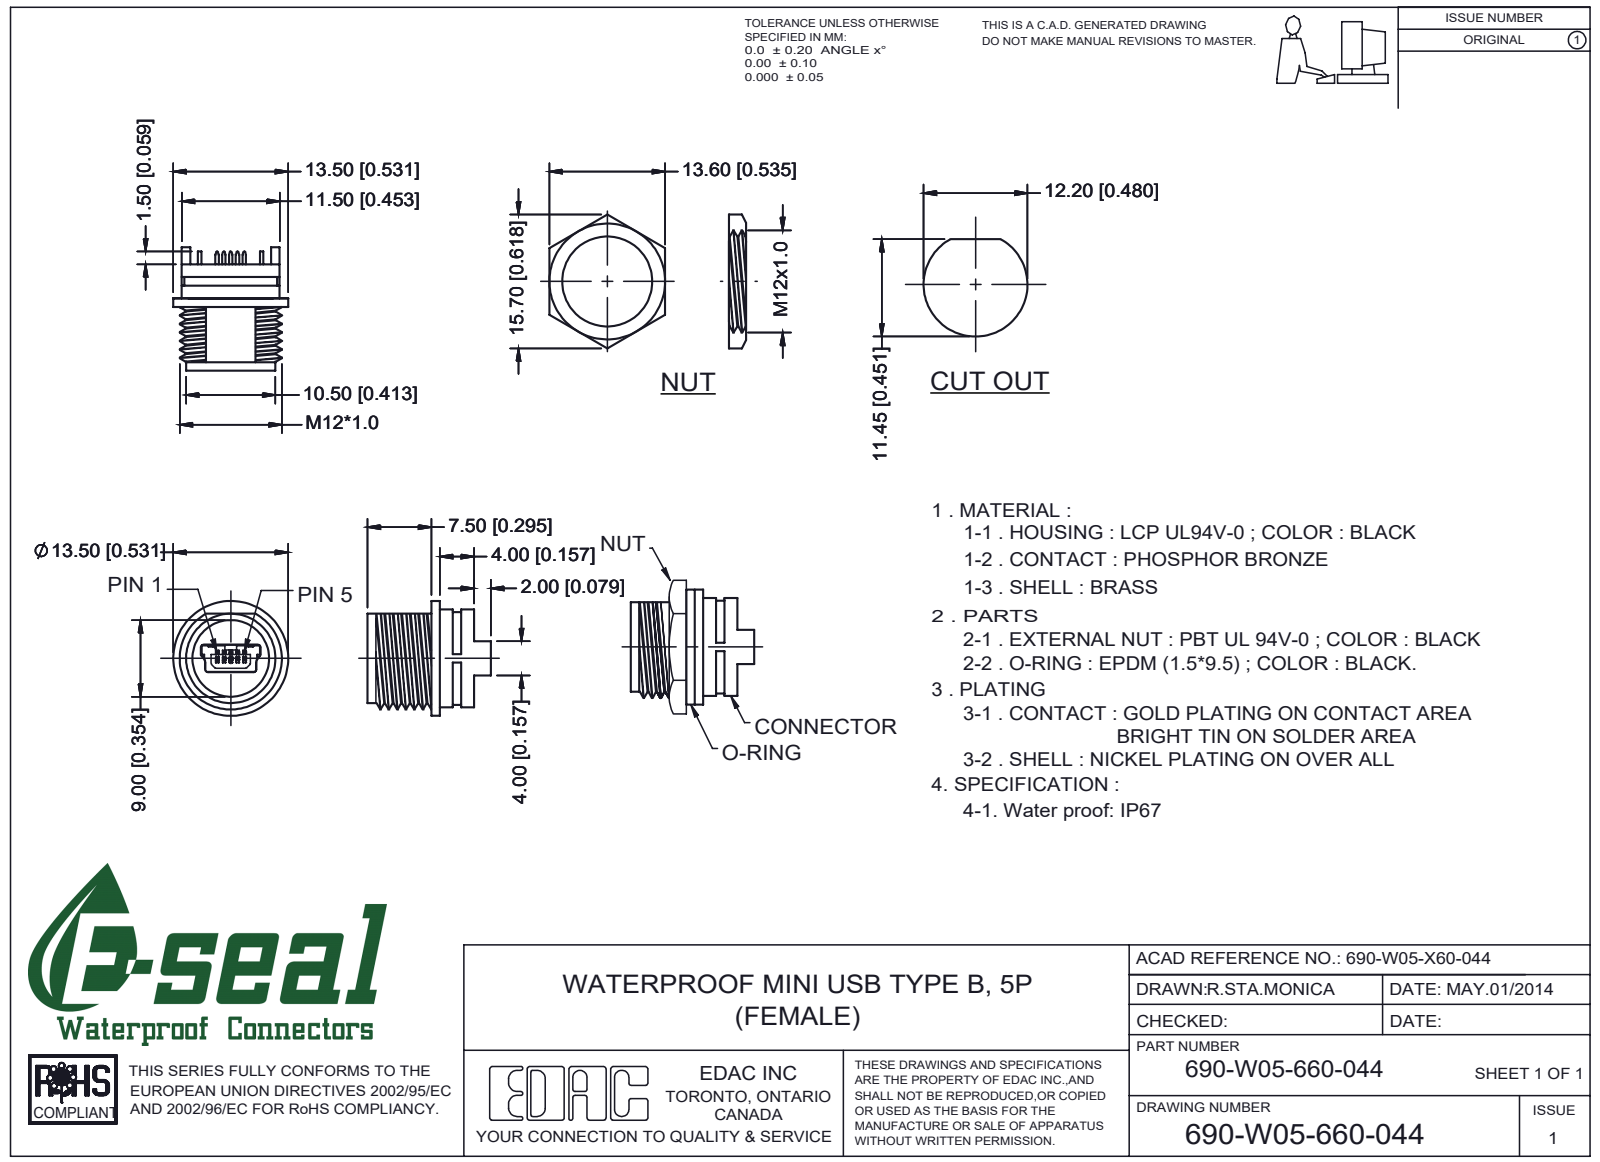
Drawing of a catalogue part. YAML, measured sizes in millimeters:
part_name: "690-W05-660-044"
step_written_by: "SolidWorks 2020 (AUTOMOTIVE_DESIGN)"
units: millimeters
bodies: {solids: 1, faces: 885, planar: 593, cylindrical: 235, other: 57}
overall_size: [15.7, 14.5, 14.2]
volume: 913
surface_area: 2247
round_holes:
  - {diameter: 9, count: 1}
  - {diameter: 9.5, count: 1}
round_bosses_or_shafts:
  - {diameter: 13.5, count: 1}
  - {diameter: 12, count: 1}
  - {diameter: 11.5, count: 1}
  - {diameter: 10.9, count: 1}
  - {diameter: 10.5, count: 1}
partial_cylinders:
  - {radius: 0.2, count: 53}
  - {radius: 0.15, count: 23}
  - {radius: 0.4, count: 12}
  - {radius: 0.6, count: 11}
  - {radius: 0.55, count: 8}
  - {radius: 0.3, count: 6}
  - {radius: 0.12, count: 5}
  - {radius: 0.19, count: 4}
face_to_face_distances: [2.95, 0.4, 3.2, 3.95, 5.45, 3.5, 1.5, 2.25, 0.75, 4]
